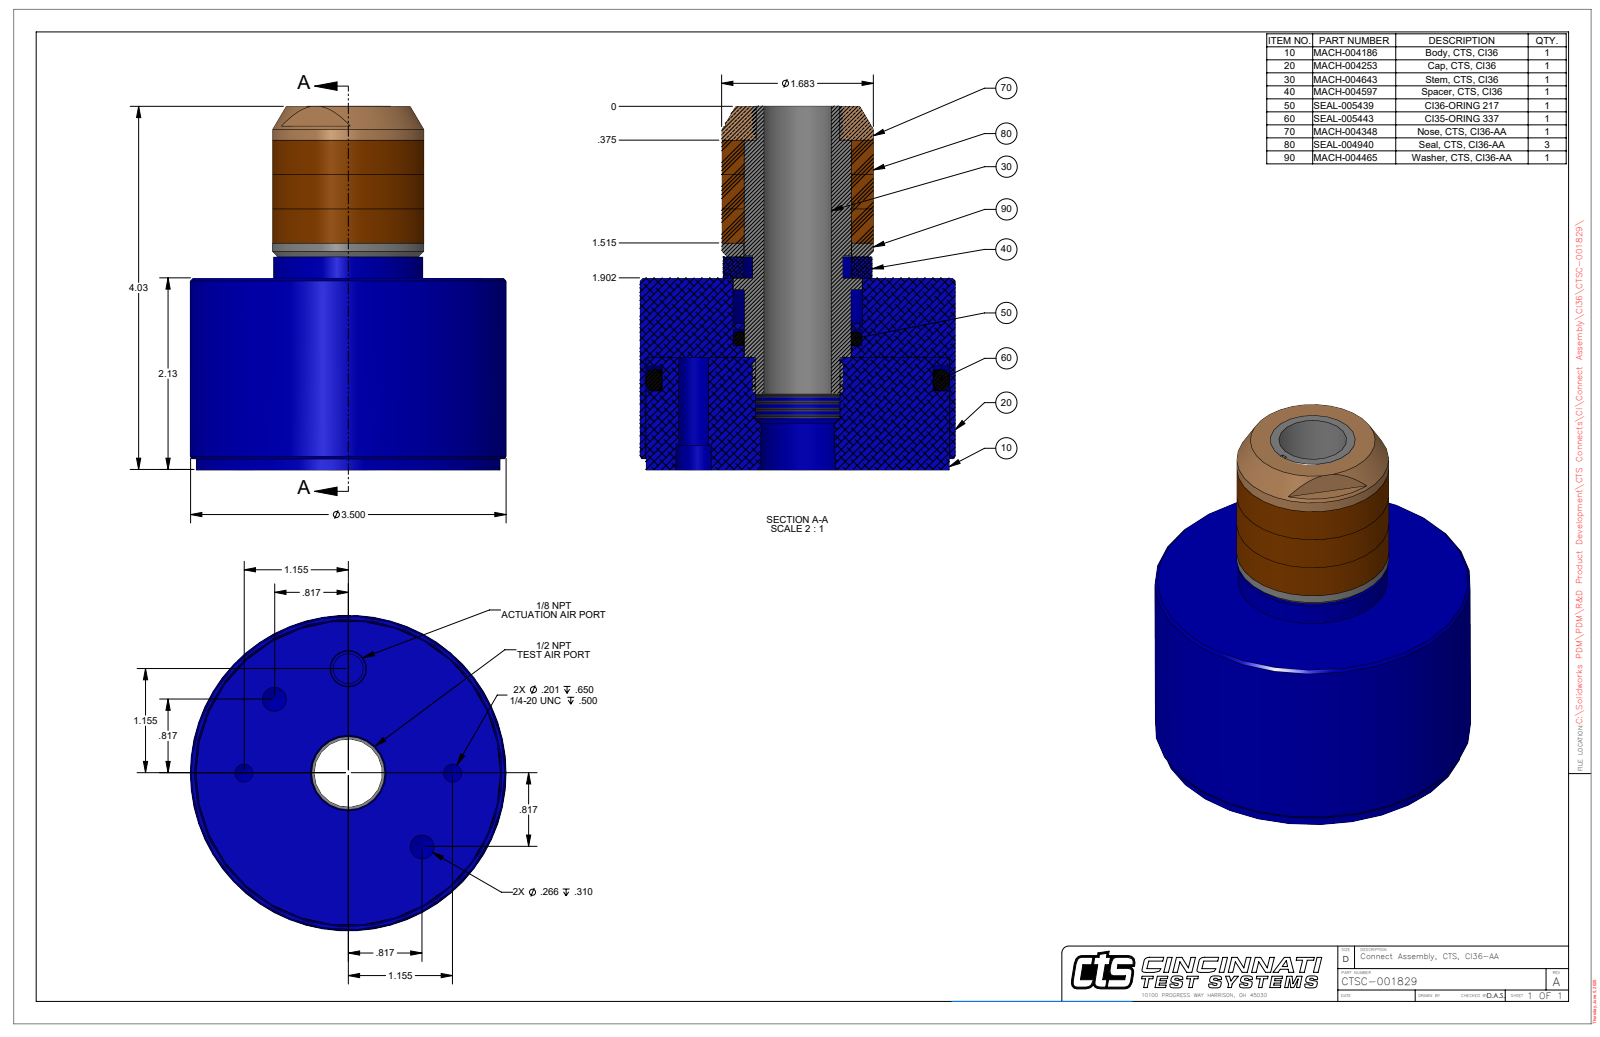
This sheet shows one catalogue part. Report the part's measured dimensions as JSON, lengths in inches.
{"part_name": "CTSC-001829", "step_written_by": "SolidWorks 2023 (AUTOMOTIVE_DESIGN)", "units": "inches", "bodies": {"solids": 1, "faces": 75, "planar": 20, "cylindrical": 29, "other": 26}, "overall_size": [4.032, 3.5, 3.5], "volume_in3": 22.34, "surface_area_in2": 78.9, "round_holes": [[0.201, 2], [0.266, 2], [0.332, 1], [0.75, 1], [0.937, 1], [1.438, 1], [3.373, 1]], "round_bosses_or_shafts": [[3.5, 1], [3.365, 1], [1.683, 1], [1.656, 1], [1.427, 1]], "partial_cylinders_radius": [[0.461, 1]], "face_to_face_distances": [2.125, 4.027, 1.902, 0.844, 1.281, 3.183, 0.125, 0.719, 2, 3.902], "hole_center_spacings": [0.884, 1.155, 2.134, 1.155, 1.633, 2.309, 2.31]}
